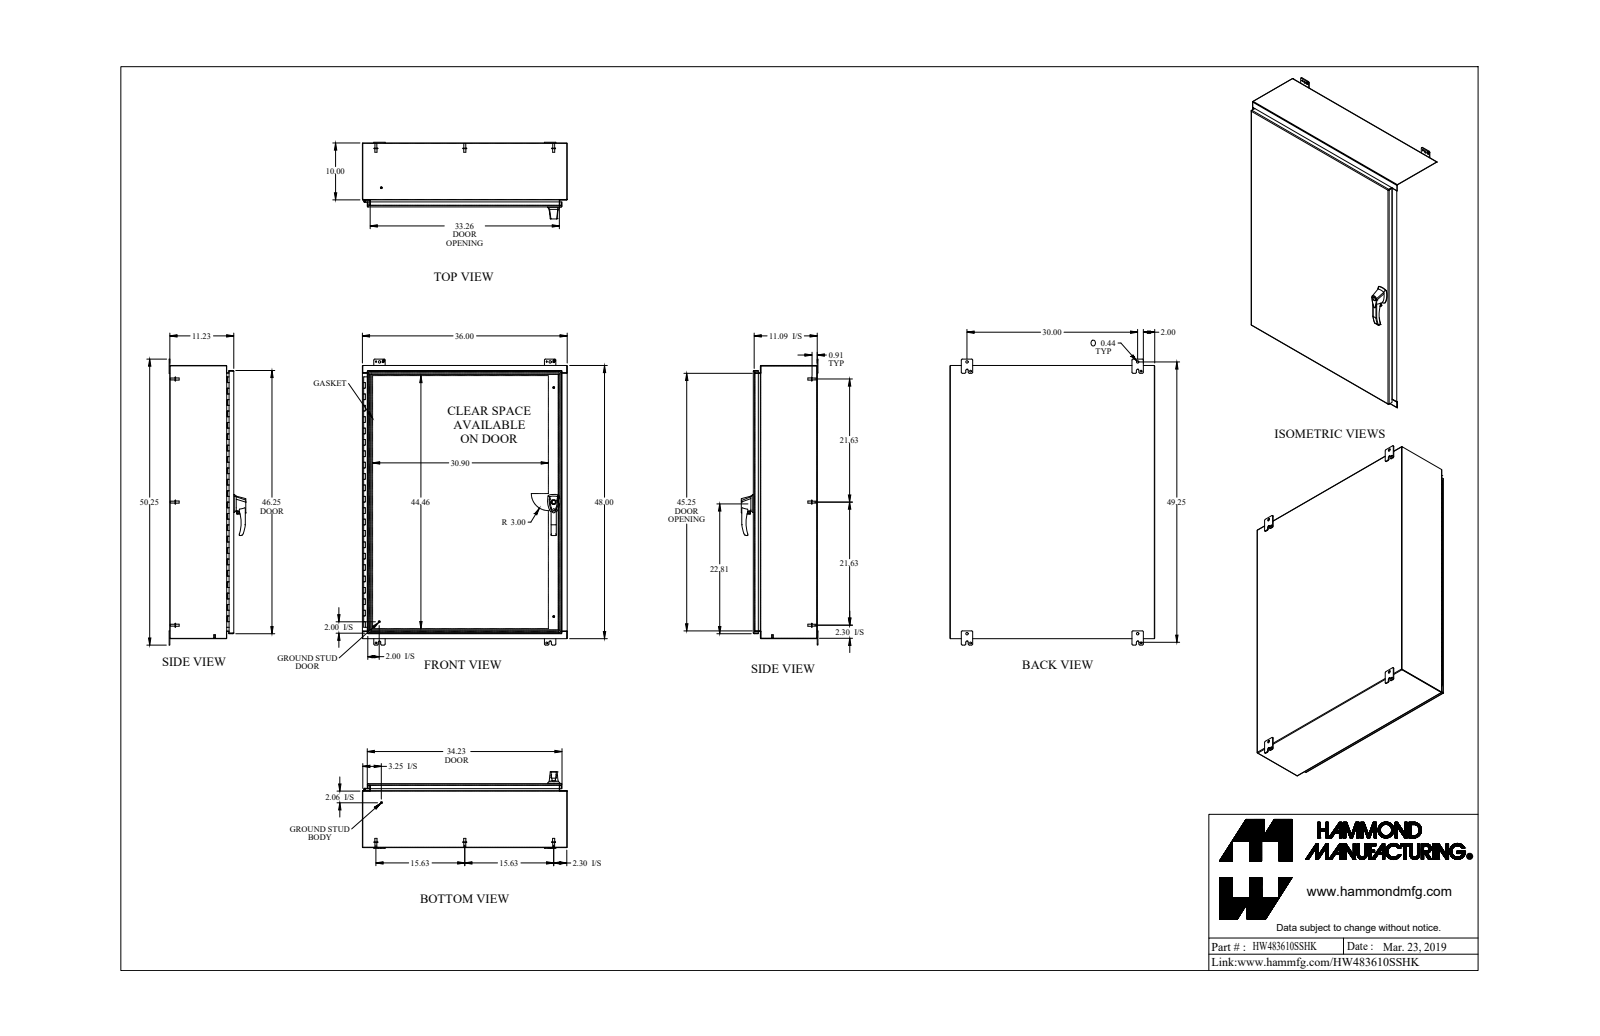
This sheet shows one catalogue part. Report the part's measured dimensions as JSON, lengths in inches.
{"part_name": "HW483610SSHK", "step_written_by": "SolidWorks 2018 (AUTOMOTIVE_DESIGN)", "units": "inches", "bodies": {"solids": 48, "faces": 1592, "planar": 761, "cylindrical": 693, "other": 138}, "overall_size": [50.25, 36, 13.473], "volume_in3": 484.1, "surface_area_in2": 11925, "round_holes": [[0.176, 6], [0.313, 5], [0.25, 3], [0.265, 3], [0.413, 3], [0.196, 2], [0.256, 2], [0.394, 2], [0.437, 2], [0.187, 1], [0.233, 1], [0.33, 1]], "round_bosses_or_shafts": [[0.375, 13], [0.65, 8], [0.332, 8], [0.25, 7], [0.156, 6], [1, 3], [0.51, 3], [0.63, 2]], "partial_cylinders_radius": [[0.25, 27], [0.188, 20], [0.036, 14], [0.108, 14], [0.06, 12], [0.125, 9], [0.218, 8], [0.03, 6]], "face_to_face_distances": [0.072, 11.138, 11.066, 0.095, 11.233, 11.161, 35.928, 47.928, 35.856, 36], "hole_center_spacings": [1.111, 20.118, 20.119, 40.237, 20.119, 30, 30.665, 38.744]}
